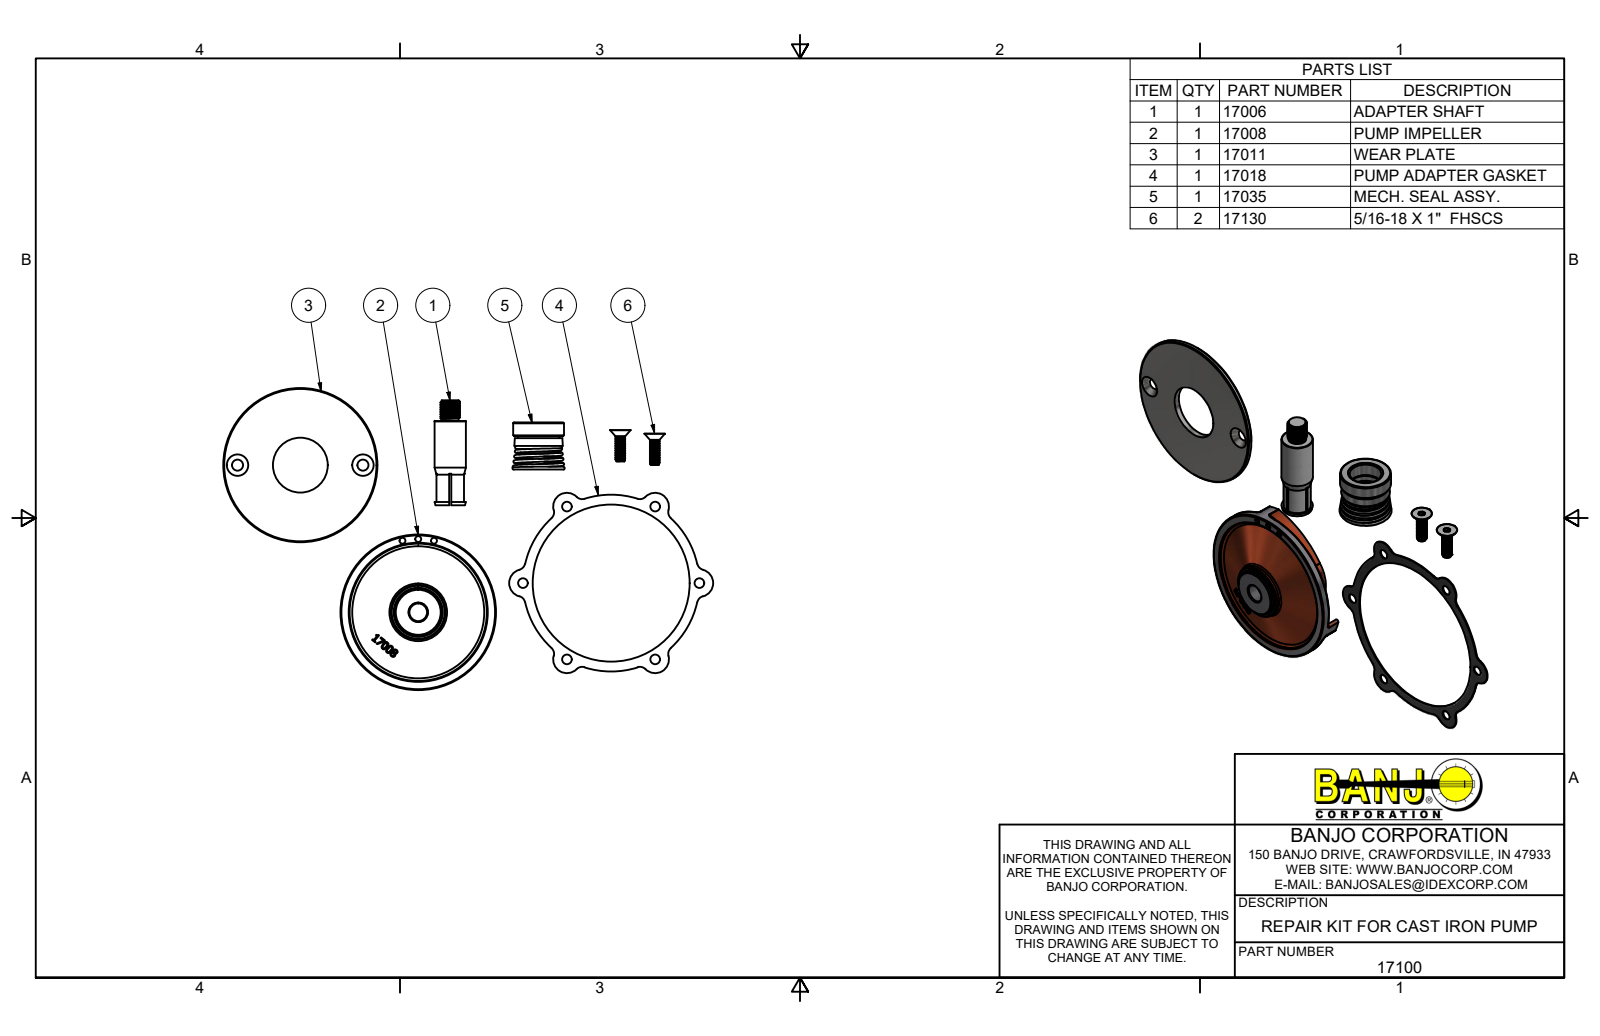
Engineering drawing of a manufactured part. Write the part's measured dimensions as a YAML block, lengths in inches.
part_name: "17100; 17006; 17008; 17011 (+3 more)"
step_written_by: "Autodesk Inventor 2019 (AUTOMOTIVE_DESIGN)"
units: inches
bodies: {solids: 8, faces: 660, planar: 109, cylindrical: 218, other: 333}
overall_size: [15.614, 9.618, 2.001]
volume: 12.26
surface_area: 155
round_holes:
  - {diameter: 0.313, count: 6}
  - {diameter: 0.187, count: 3}
  - {diameter: 1.125, count: 2}
  - {diameter: 0.565, count: 1}
  - {diameter: 0.754, count: 1}
  - {diameter: 0.772, count: 1}
  - {diameter: 1, count: 1}
  - {diameter: 1.063, count: 1}
  - {diameter: 1.75, count: 1}
  - {diameter: 4.375, count: 1}
  - {diameter: 5.01, count: 1}
round_bosses_or_shafts:
  - {diameter: 0.268, count: 28}
  - {diameter: 0.313, count: 2}
  - {diameter: 4.957, count: 1}
  - {diameter: 4.91, count: 1}
  - {diameter: 1.75, count: 1}
  - {diameter: 1.625, count: 1}
  - {diameter: 1.563, count: 1}
  - {diameter: 1.5, count: 1}
partial_cylinders:
  - {radius: 0.25, count: 12}
  - {radius: 0.062, count: 9}
  - {radius: 0.437, count: 6}
  - {radius: 0.048, count: 3}
  - {radius: 0.063, count: 3}
  - {radius: 0.937, count: 3}
  - {radius: 1.125, count: 3}
  - {radius: 2.25, count: 3}
face_to_face_distances: [0.193, 0.031, 0.049, 0.144, 0.113, 0.08, 0.326, 0.213, 0.182, 0.133]
hole_center_spacings: [2.813, 4.872, 2.333, 0.503, 4.871, 5.625, 1, 2.812]
